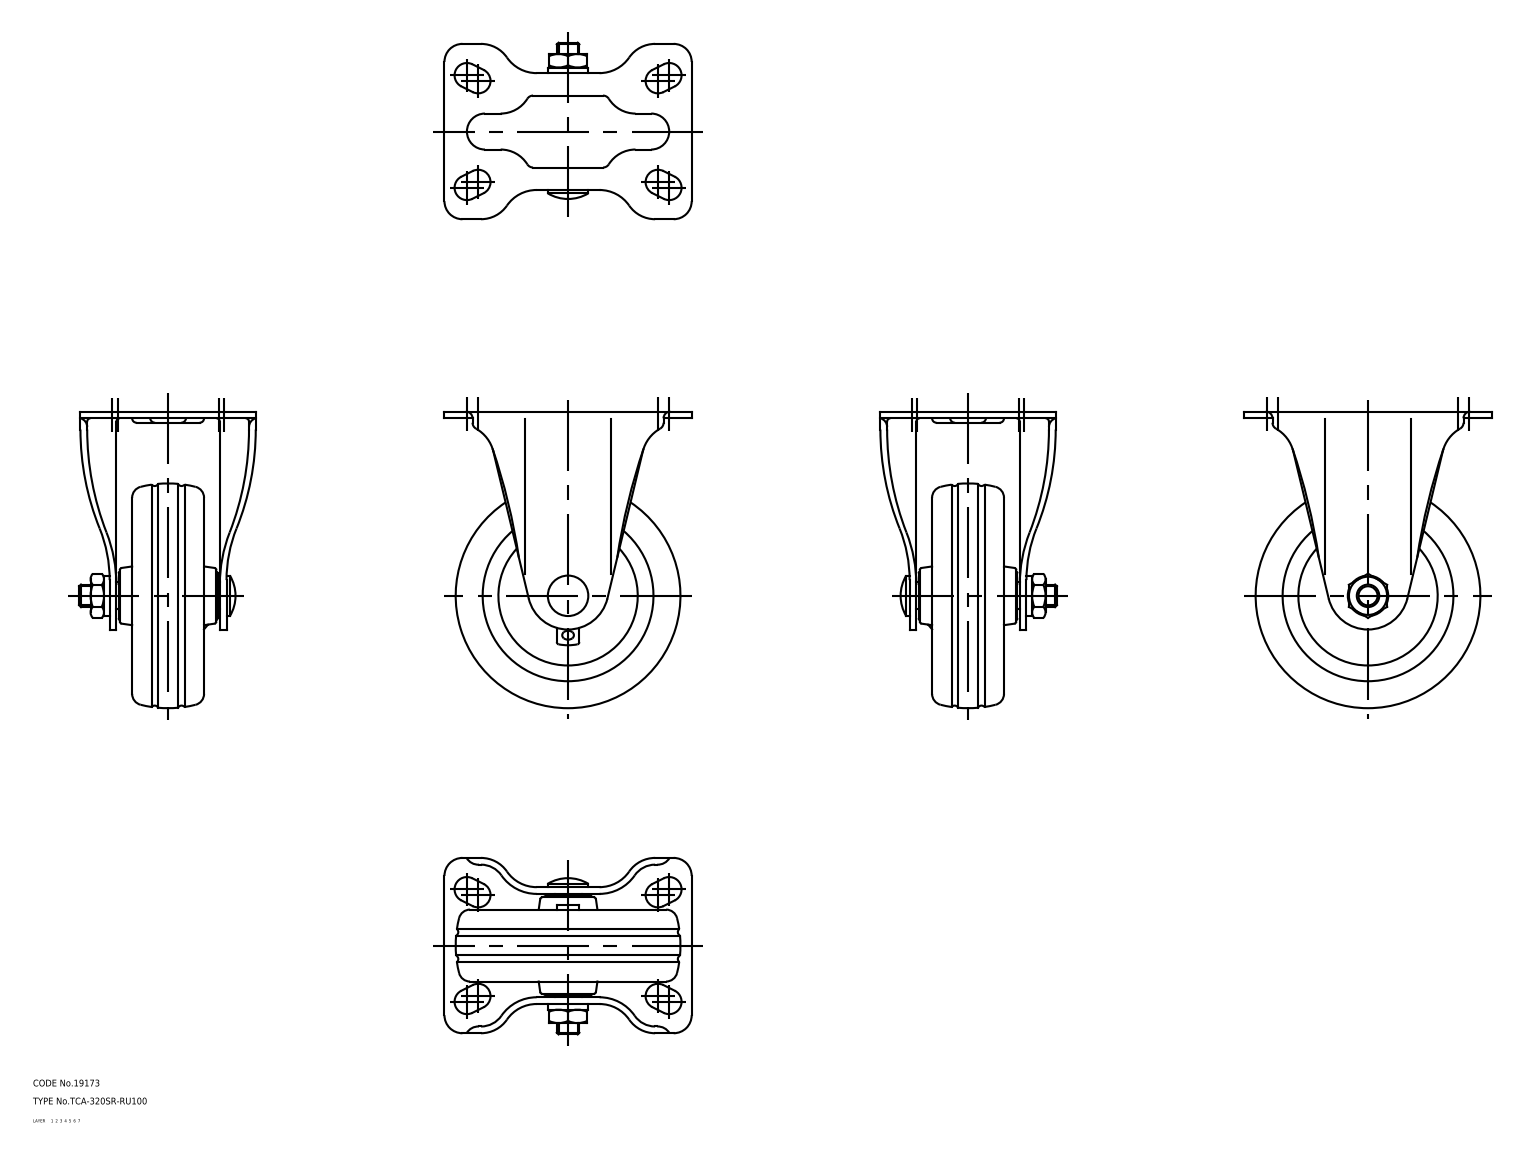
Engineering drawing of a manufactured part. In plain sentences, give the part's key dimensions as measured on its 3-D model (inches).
The part is named "67125322; 67125335; 67125348; 67125361 (+2 more)". Its 3-D file was written by "CADfix (AUTOMOTIVE_DESIGN)". It is 3 solids with 269 faces: 0 planar, 0 cylindrical and 269 other. Overall it measures 5.197 by 4.331 by 3.091 inches. Its volume is 15.83 cubic inches and its surface area 107.1 square inches.
